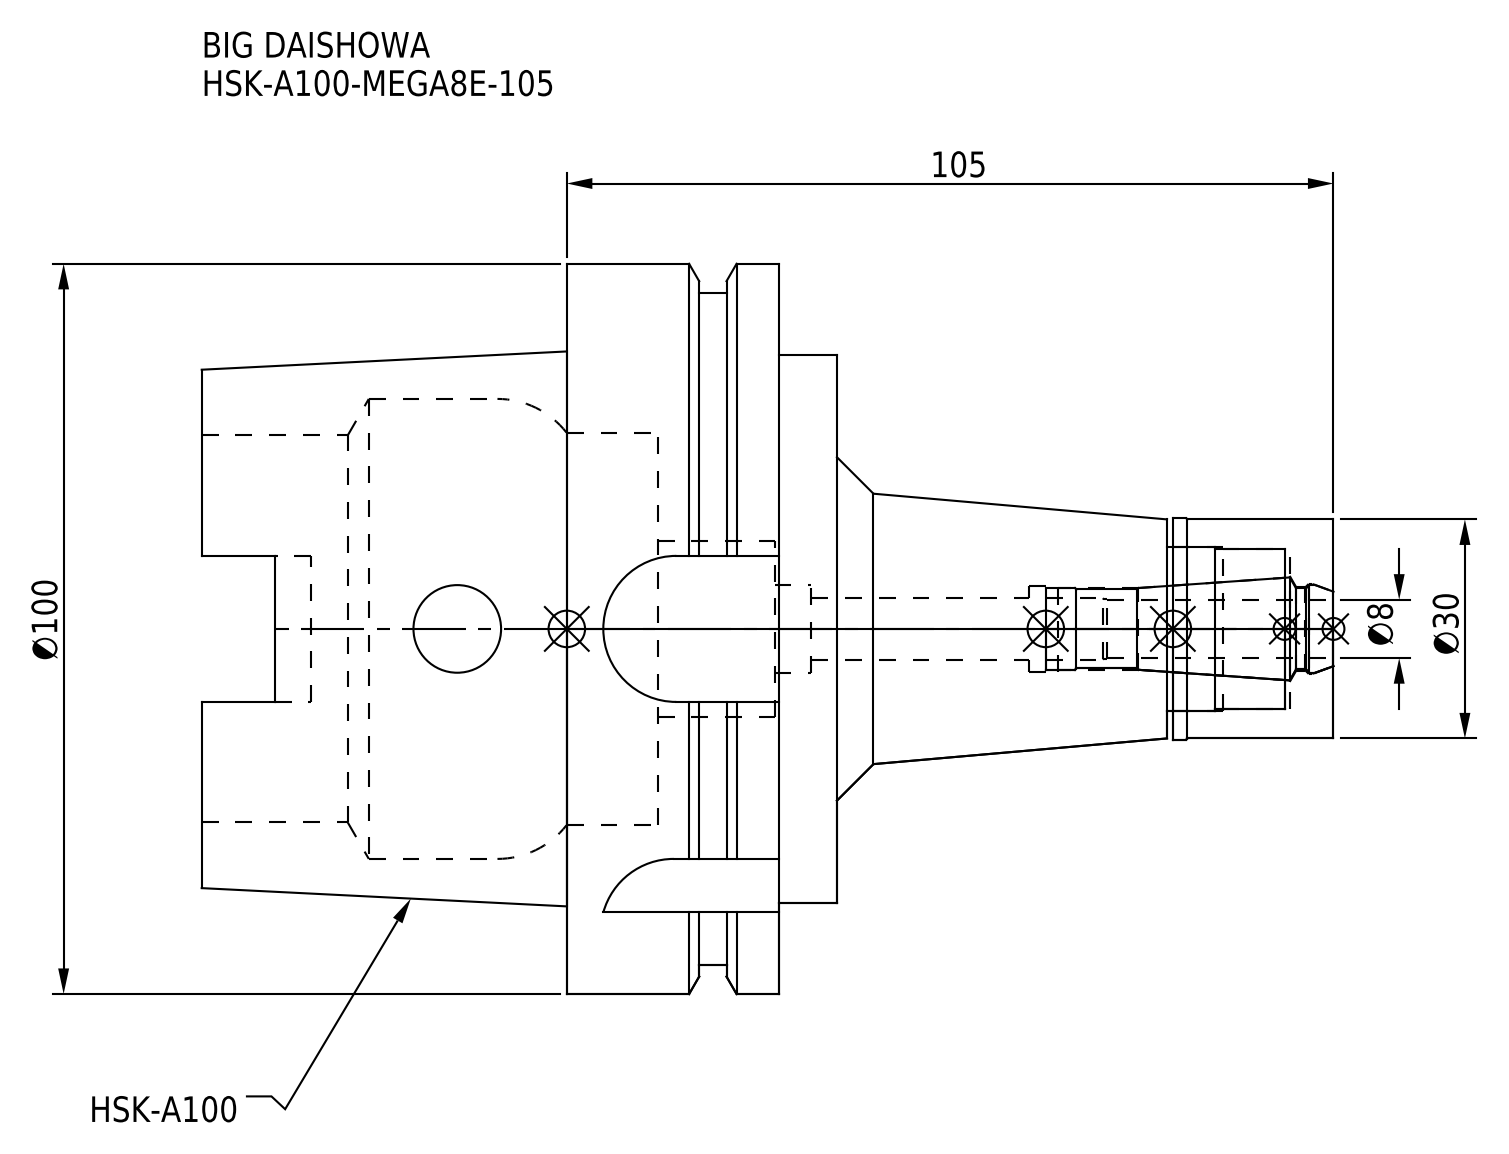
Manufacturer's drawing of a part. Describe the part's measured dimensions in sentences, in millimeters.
The part is named "HSK-A100-MEGA8E-105_1.stp; DXF_TEMP_ASSY_ASM_4_ASM.stp; HA100ME08105-080_ASM.stp; HSK-A100-MEGA8E-105-080-FreeParts (+3 more)". Its 3-D file was written by "SolidWorks 2019 (CONFIG_CONTROL_DESIGN)". It is 2 solids with 126 faces: 42 planar, 56 cylindrical and 28 other. Overall it measures 155 by 100 by 100 millimeters. Its volume is 340 283 cubic millimeters and its surface area 63 972 square millimeters. Round holes: 2 of diameter 12, 1 of diameter 8.4, 1 of diameter 11.2, 1 of diameter 11.4, 1 of diameter 11.8, 1 of diameter 12.3, 1 of diameter 22, 1 of diameter 22.5, 1 of diameter 24, 1 of diameter 53, 1 of diameter 53.8, 1 of diameter 63. Round bosses or shafts: 1 of diameter 100, 1 of diameter 92, 1 of diameter 75, 1 of diameter 30.3, 1 of diameter 30. Partial cylindrical surfaces (rounded edges, fillets, slot ends): 4 of radius 4.88, 4 of radius 10. The main face-to-face distances are 29, 8, 37, 24.55, 16.55, 12.45, 87, 79, 62.45, 50.
